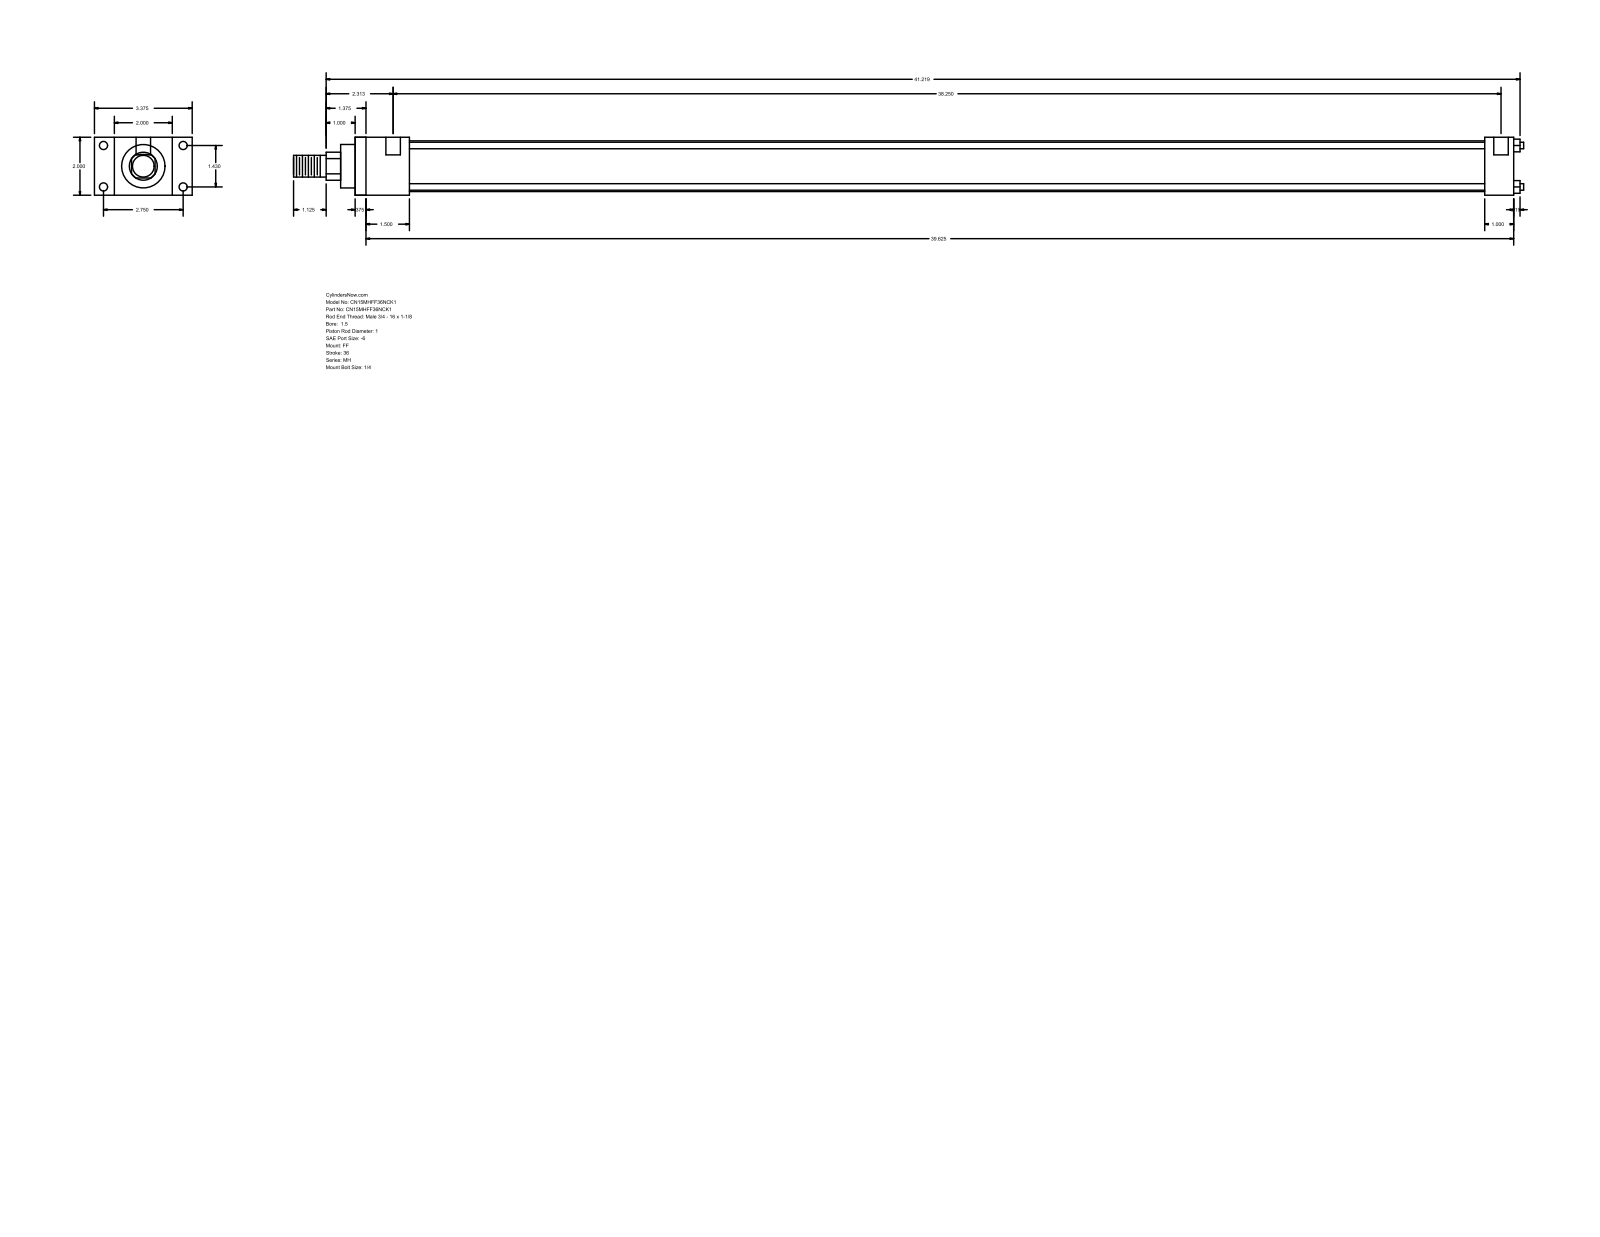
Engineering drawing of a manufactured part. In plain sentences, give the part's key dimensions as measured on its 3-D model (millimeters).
The part is named "MH_FF__0150_1". Its 3-D file was written by "GSSL Pune (CONFIG_CONTROL_DESIGN)". It is 0 solids with 92 faces: 64 planar, 28 cylindrical and 0 other. Overall it measures 1078.71 by 85.72 by 50.8 millimeters. Round holes: 4 of diameter 5.56, 4 of diameter 7.14, 2 of diameter 12.7. Round bosses or shafts: 4 of diameter 5.71, 1 of diameter 44.45, 1 of diameter 38.1, 1 of diameter 25.4, 1 of diameter 19.05. Partial cylindrical surfaces (rounded edges, fillets, slot ends): 1 of radius 12.29. The main face-to-face distances are 50.8, 1016, 9.52, 1006.48, 25.4, 17.46, 68.26, 47.63, 38.11, 968.37. The hole center spacings are 36.32, 69.84, 78.72, 974.73, 3.18, 971.55.
